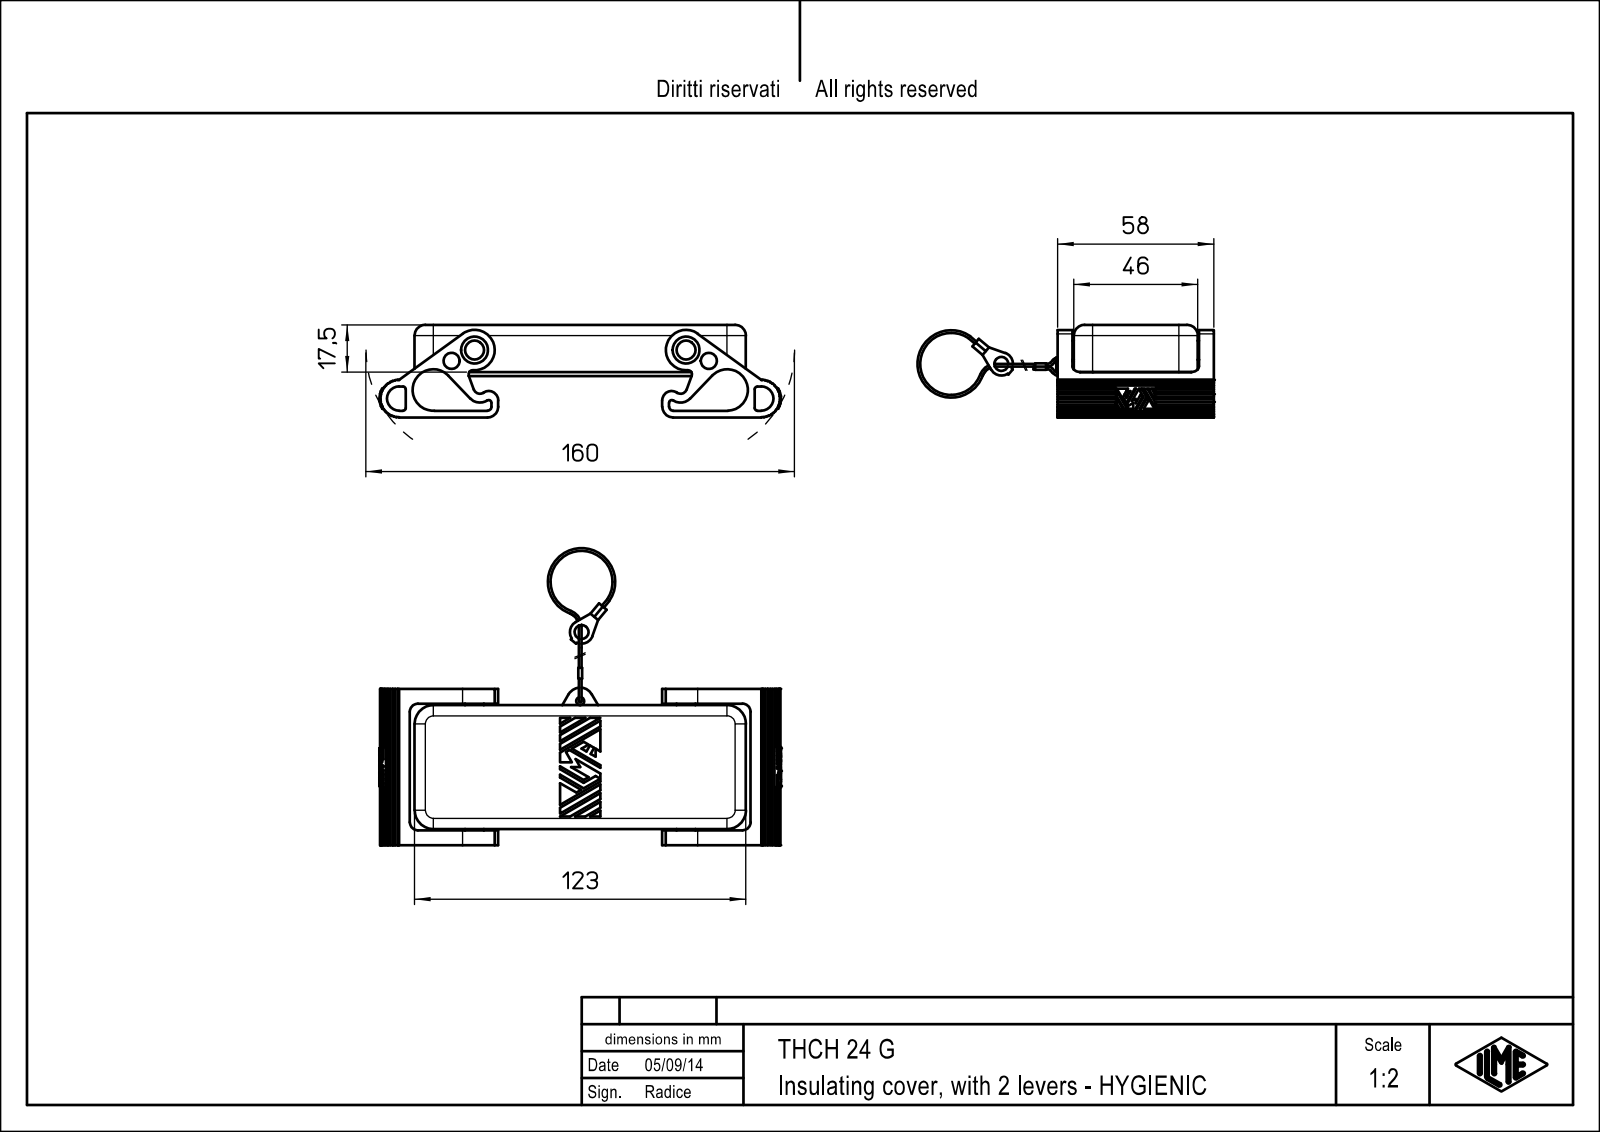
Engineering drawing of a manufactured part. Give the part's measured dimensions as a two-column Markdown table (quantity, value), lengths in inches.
| quantity | value |
| --- | --- |
| part name | THCH_24_G |
| STEP written by | Creo Elements/Direct Modeling 18.0B 02-Dec-2011 (C) Parametric Technology GmbH (AUTOMOTIVE_DESIGN) |
| units | inches |
| bodies | 1 solid, 671 faces (436 planar, 215 cylindrical, 20 other) |
| overall size | 5.87 × 2.303 × 1.354 |
| volume | 4.558 in³ |
| surface area | 59.7 in² |
| round holes (diameter × count) | 0.236 × 2, 0.394 × 2, 0.118 × 1 |
| round bosses / shafts (diameter × count) | 0.276 × 2 |
| partial cylindrical surfaces (radius × count) | 0.039 × 16, 0.059 × 16, 0.02 × 12, 0.071 × 8, 0.157 × 6, 0.276 × 6, 0.118 × 4, 0.04 × 2 |
| main face-to-face distances | 0.217, 1.831, 0.236, 0.02, 1.614, 1.594, 0.098, 0.453, 2.047, 2.067 |
| hole center spacings | 0.37, 3.429, 3.091, 3.76 |
